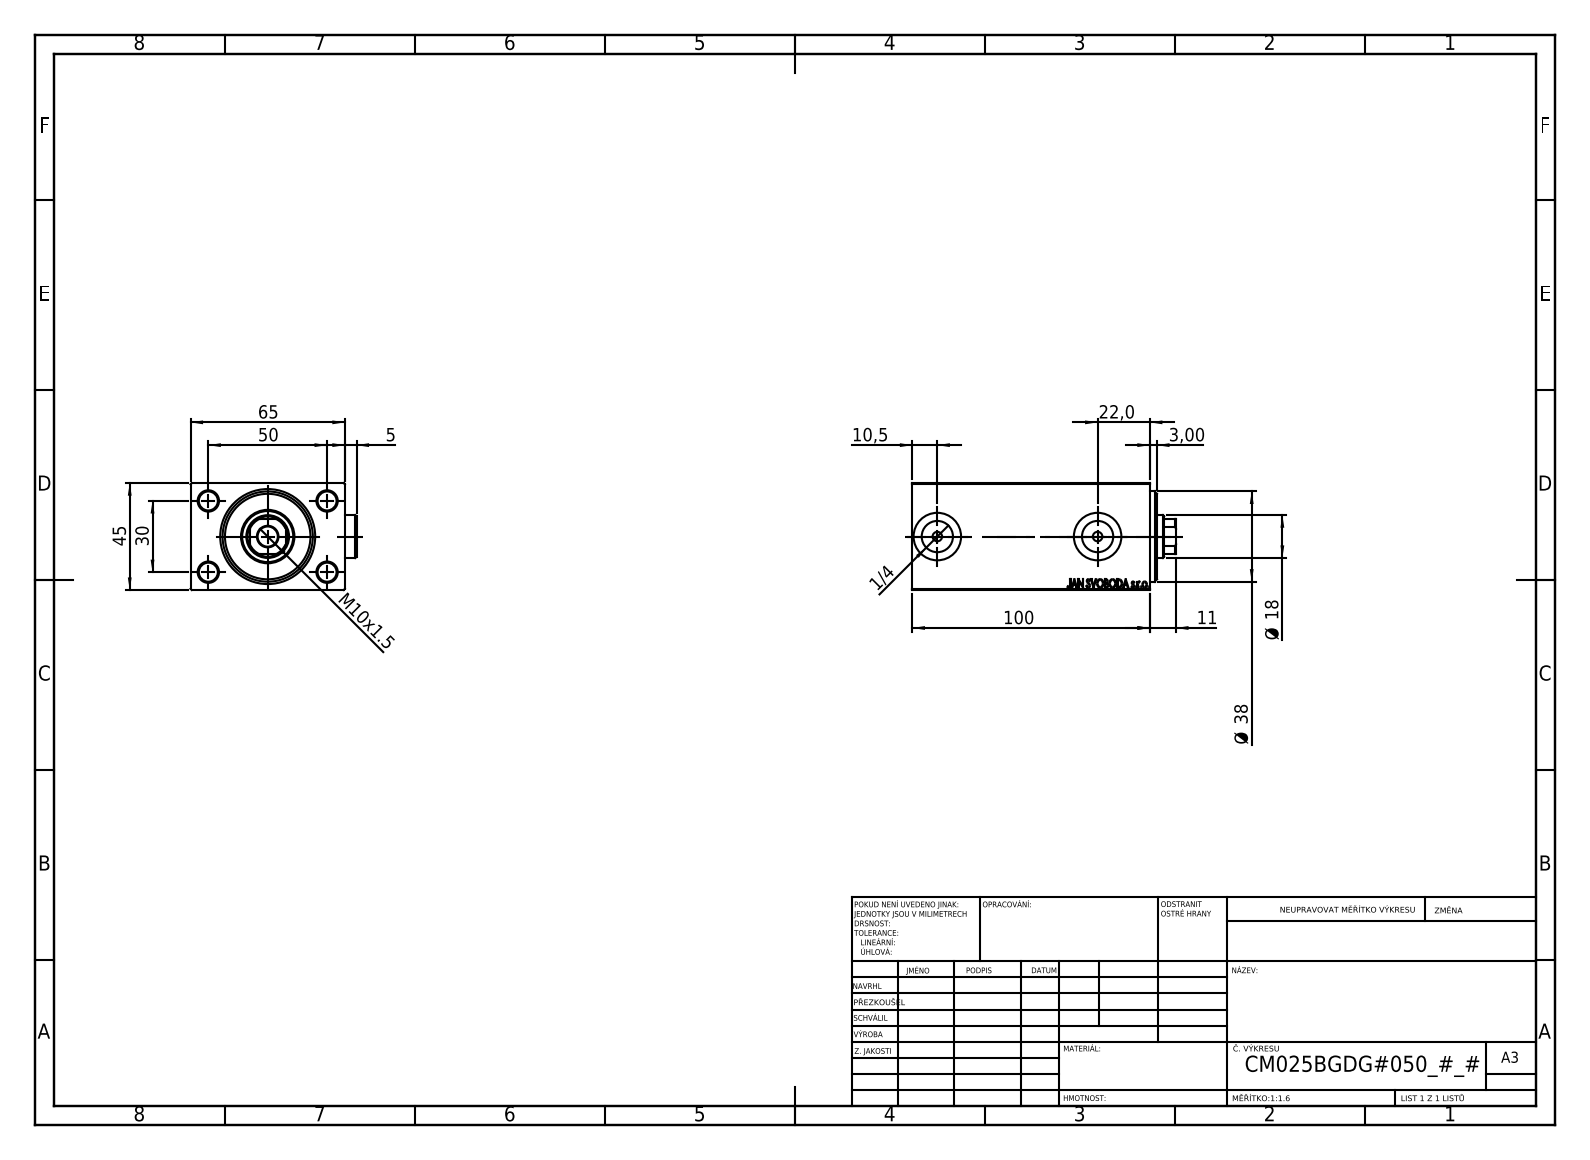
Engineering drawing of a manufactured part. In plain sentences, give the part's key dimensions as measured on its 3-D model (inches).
The part is named "V450CM_B_Body; Zatka_OIL_PORT; V450CM_B_VCP; V450CM_VC_B". Its 3-D file was written by "SolidWorks 2019 (CONFIG_CONTROL_DESIGN)". It is 5 solids with 935 faces: 435 planar, 70 cylindrical and 430 other. Overall it measures 4.37 by 2.752 by 1.772 inches. Its volume is 16.66 cubic inches and its surface area 84.52 square inches. Round holes: 4 of diameter 0.315, 2 of diameter 0.157, 2 of diameter 0.518, 2 of diameter 0.787, 1 of diameter 0.335, 1 of diameter 0.709, 1 of diameter 0.846, 1 of diameter 0.886, 1 of diameter 0.984, 1 of diameter 1.063, 1 of diameter 1.496. Round bosses or shafts: 2 of diameter 0.709. Partial cylindrical surfaces (rounded edges, fillets, slot ends): 1 of radius 0.335. The main face-to-face distances are 1.772, 2.559, 0.197, 0.236, 3.937, 3.504, 2.555, 3.74, 3.701, 0.315. The hole center spacings are 1.148, 1.181, 1.969, 2.296, 2.657.
